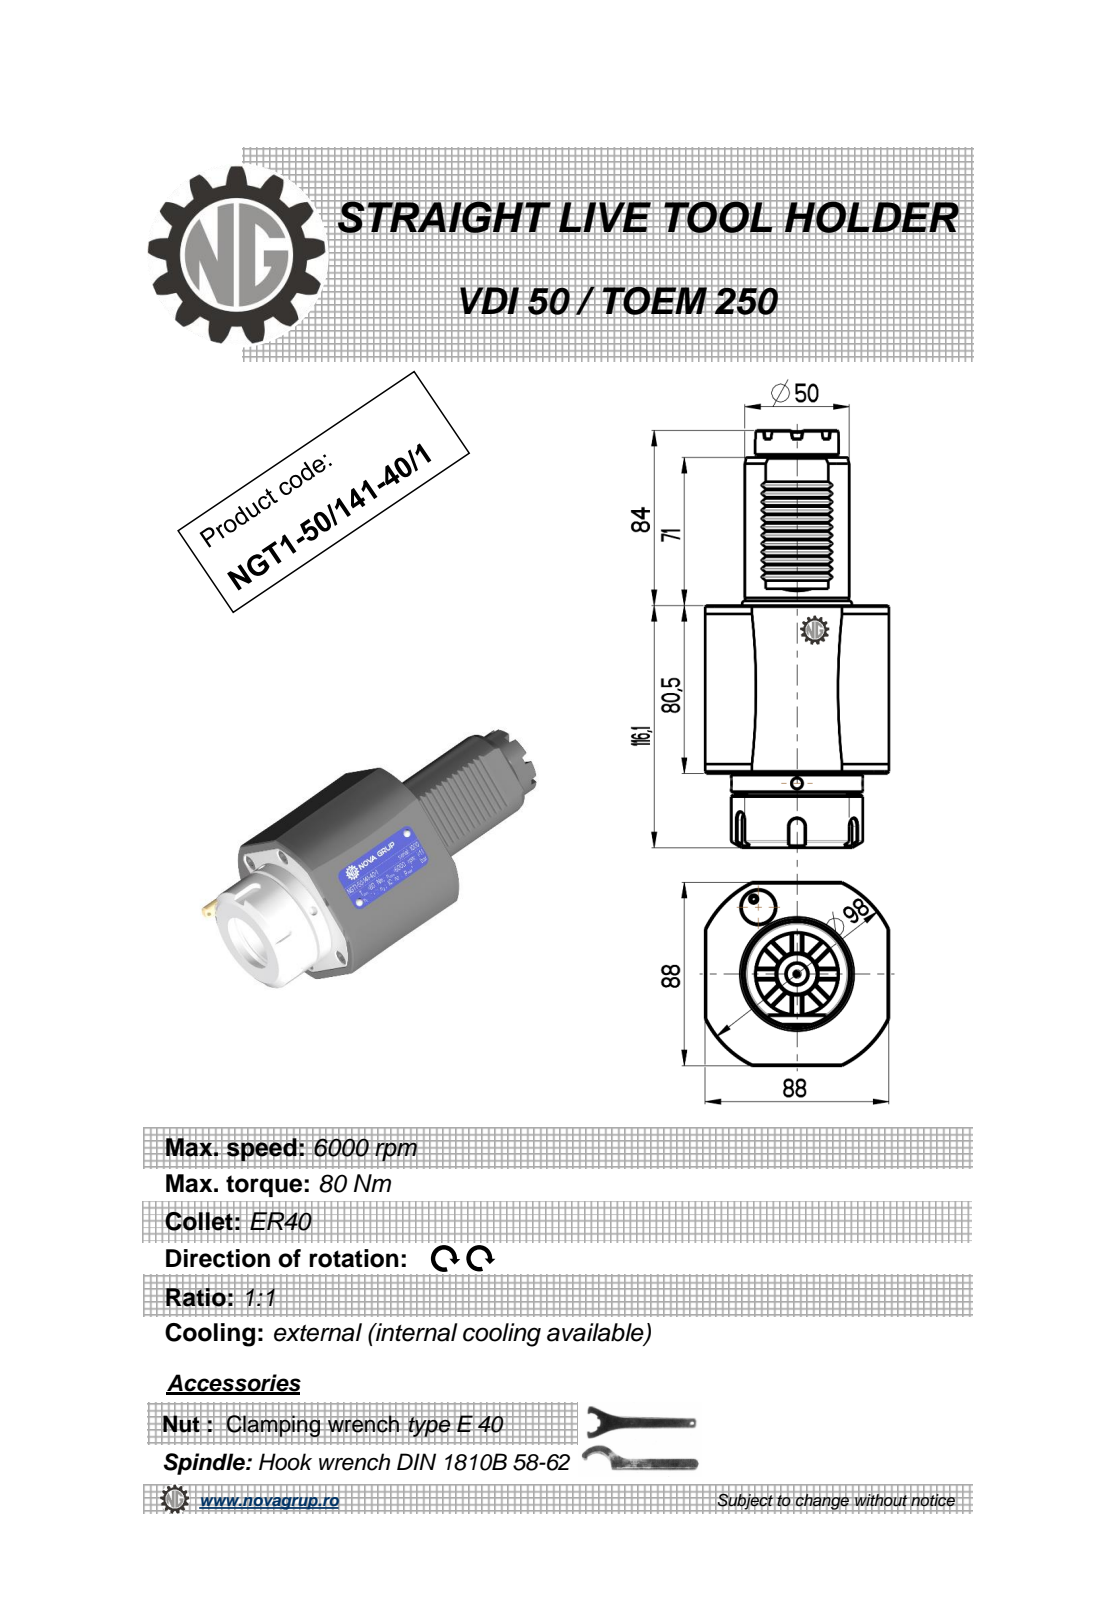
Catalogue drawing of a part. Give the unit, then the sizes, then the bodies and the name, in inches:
Units: inches
Overall size (bounding box): 7.878 × 3.528 × 3.465
Round holes (diameter × count): ⌀0.197 ×2, ⌀0.098 ×1, ⌀0.118 ×1, ⌀0.807 ×1, ⌀1.319 ×1
Round bosses / shafts (diameter × count): ⌀2.48 ×1, ⌀2.008 ×1, ⌀1.969 ×1, ⌀1.575 ×1, ⌀0.354 ×1, ⌀0.276 ×1, ⌀0.197 ×1
Partial cylindrical surfaces — rounded edges, fillets, slot ends (radius × count): R0.012 ×12, R0.148 ×5, R1.929 ×1
Main face-to-face distances: 3.465, 3.169, 0.354, 6.319, 4.571, 1.402, 4.327, 1.157, 0.244, 3.189
Hole centre spacings: 1.634
Volume: 48.88 in³ · Surface area: 103.3 in²
Bodies: 1 solid, 362 faces (151 planar, 77 cylindrical, 134 other)
Part name (STEP PRODUCT): NGT1_50_141_40_1
STEP written by: PRO/ENGINEER BY PARAMETRIC TECHNOLOGY CORPORATION, 2010280 (CONFIG_CONTROL_DESIGN)
